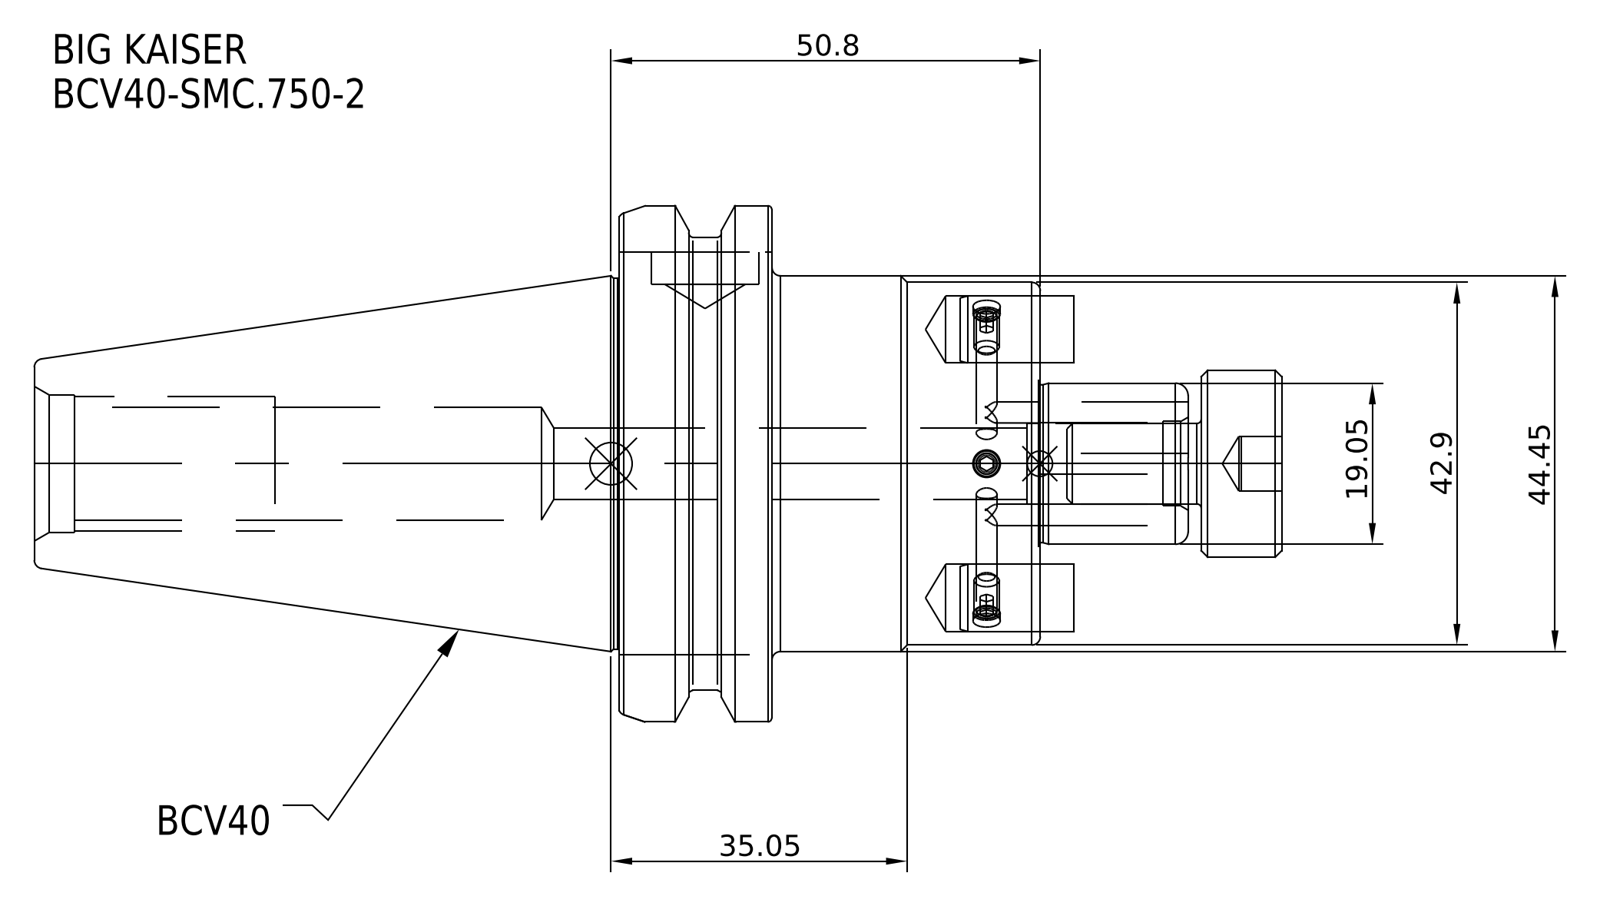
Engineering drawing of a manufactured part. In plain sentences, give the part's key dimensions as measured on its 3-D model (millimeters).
The part is named "BCV40-SMC_750-2". Its 3-D file was written by "SolidWorks 2021 (CONFIG_CONTROL_DESIGN)". It is 1 solid with 38 faces: 18 planar, 14 cylindrical and 6 other. Overall it measures 123.02 by 63.5 by 63.5 millimeters. Its volume is 168 043 cubic millimeters and its surface area 22 280 square millimeters. Round holes: 1 of diameter 8.43. Round bosses or shafts: 1 of diameter 63.5, 1 of diameter 56.36, 1 of diameter 44.45, 1 of diameter 42.9. The main face-to-face distances are 18.05, 31.75, 49.8, 119.05, 87.3, 69.25, 15.75, 16, 34.05, 103.3.
